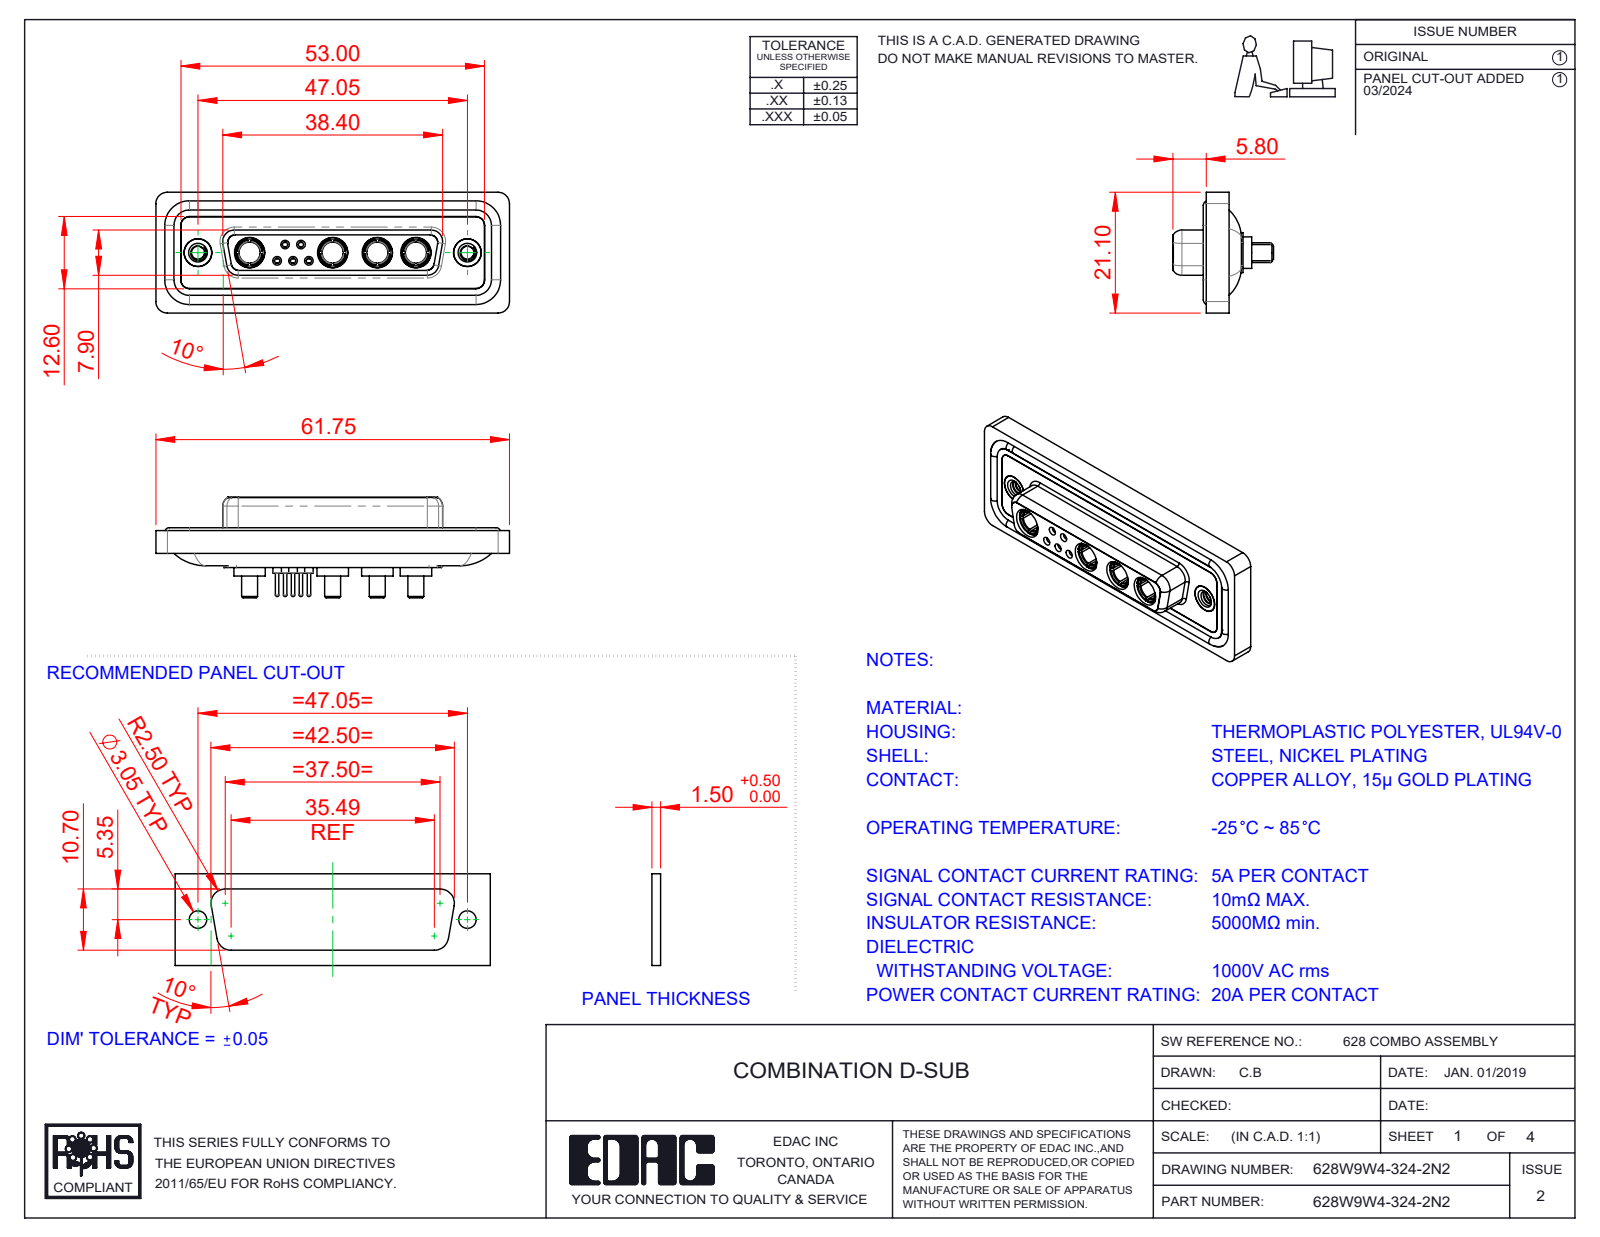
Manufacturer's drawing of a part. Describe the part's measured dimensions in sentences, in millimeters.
The part is named "Power Socket_20A S; 628Combo Contact Row 2_24; 628Combo Contact Row 1_24; 628Combo Shell Front_25 Contacts (+5 more)". Its 3-D file was written by "SolidWorks 2023 (CONFIG_CONTROL_DESIGN)". It is 20 solids with 957 faces: 296 planar, 375 cylindrical and 286 other. Overall it measures 61.75 by 21.1 by 17.55 millimeters. Its volume is 8 223 cubic millimeters and its surface area 13 562 square millimeters. Round holes: 6 of diameter 4.85, 5 of diameter 0.9, 5 of diameter 1.1, 5 of diameter 1.5, 5 of diameter 2, 4 of diameter 3.7, 4 of diameter 5.3, 3 of diameter 1.6, 2 of diameter 1.7, 2 of diameter 2.26, 2 of diameter 4, 2 of diameter 4.05. Round bosses or shafts: 6 of diameter 1.6, 5 of diameter 2.2, 5 of diameter 0.6, 4 of diameter 5.5, 4 of diameter 5.2, 4 of diameter 4.96, 4 of diameter 4.75, 4 of diameter 3.75. Partial cylindrical surfaces (rounded edges, fillets, slot ends): 22 of radius 1.5, 18 of radius 2, 8 of radius 1.35, 8 of radius 1.6, 4 of radius 0.25, 4 of radius 0.5, 4 of radius 0.6, 4 of radius 0.65. The main face-to-face distances are 0.4, 1.8, 7.45, 5.65, 0.5, 7.05, 6.6, 1.6, 1.1, 2.9. The hole center spacings are 3.16, 2.77, 5.03, 2.76, 4.4, 5.02, 5.54, 5.73.
